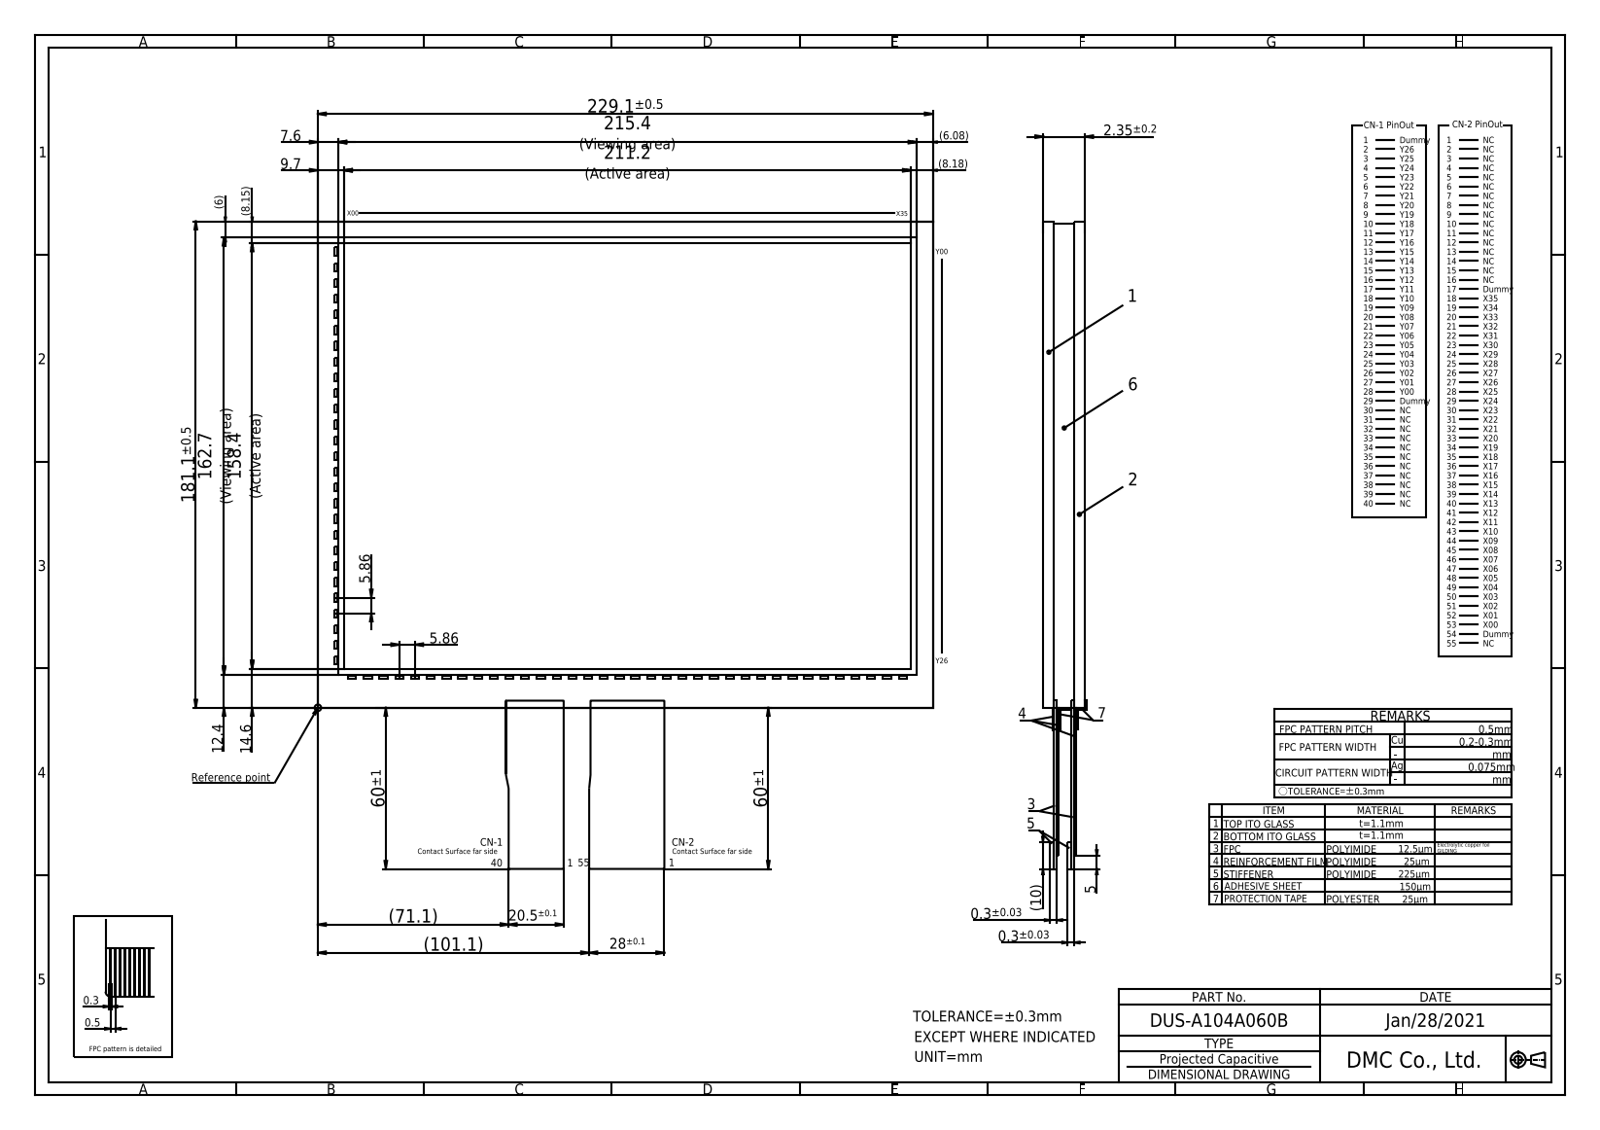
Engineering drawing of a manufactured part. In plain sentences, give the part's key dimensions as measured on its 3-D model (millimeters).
The part is named "DUS-A104A060B". Its 3-D file was written by "Autodesk Inventor 2020 (CONFIG_CONTROL_DESIGN)". It is 1 solid with 422 faces: 418 planar, 4 cylindrical and 0 other. Overall it measures 320.74 by 277.32 by 2.35 millimeters. Its volume is 97 755 cubic millimeters and its surface area 90 977 square millimeters. Partial cylindrical surfaces (rounded edges, fillets, slot ends): 4 of radius 0.2. The main face-to-face distances are 2.35, 1.1, 1.15, 1.2, 1.25, 1, 2.25, 181.1, 0.8, 0.7.
